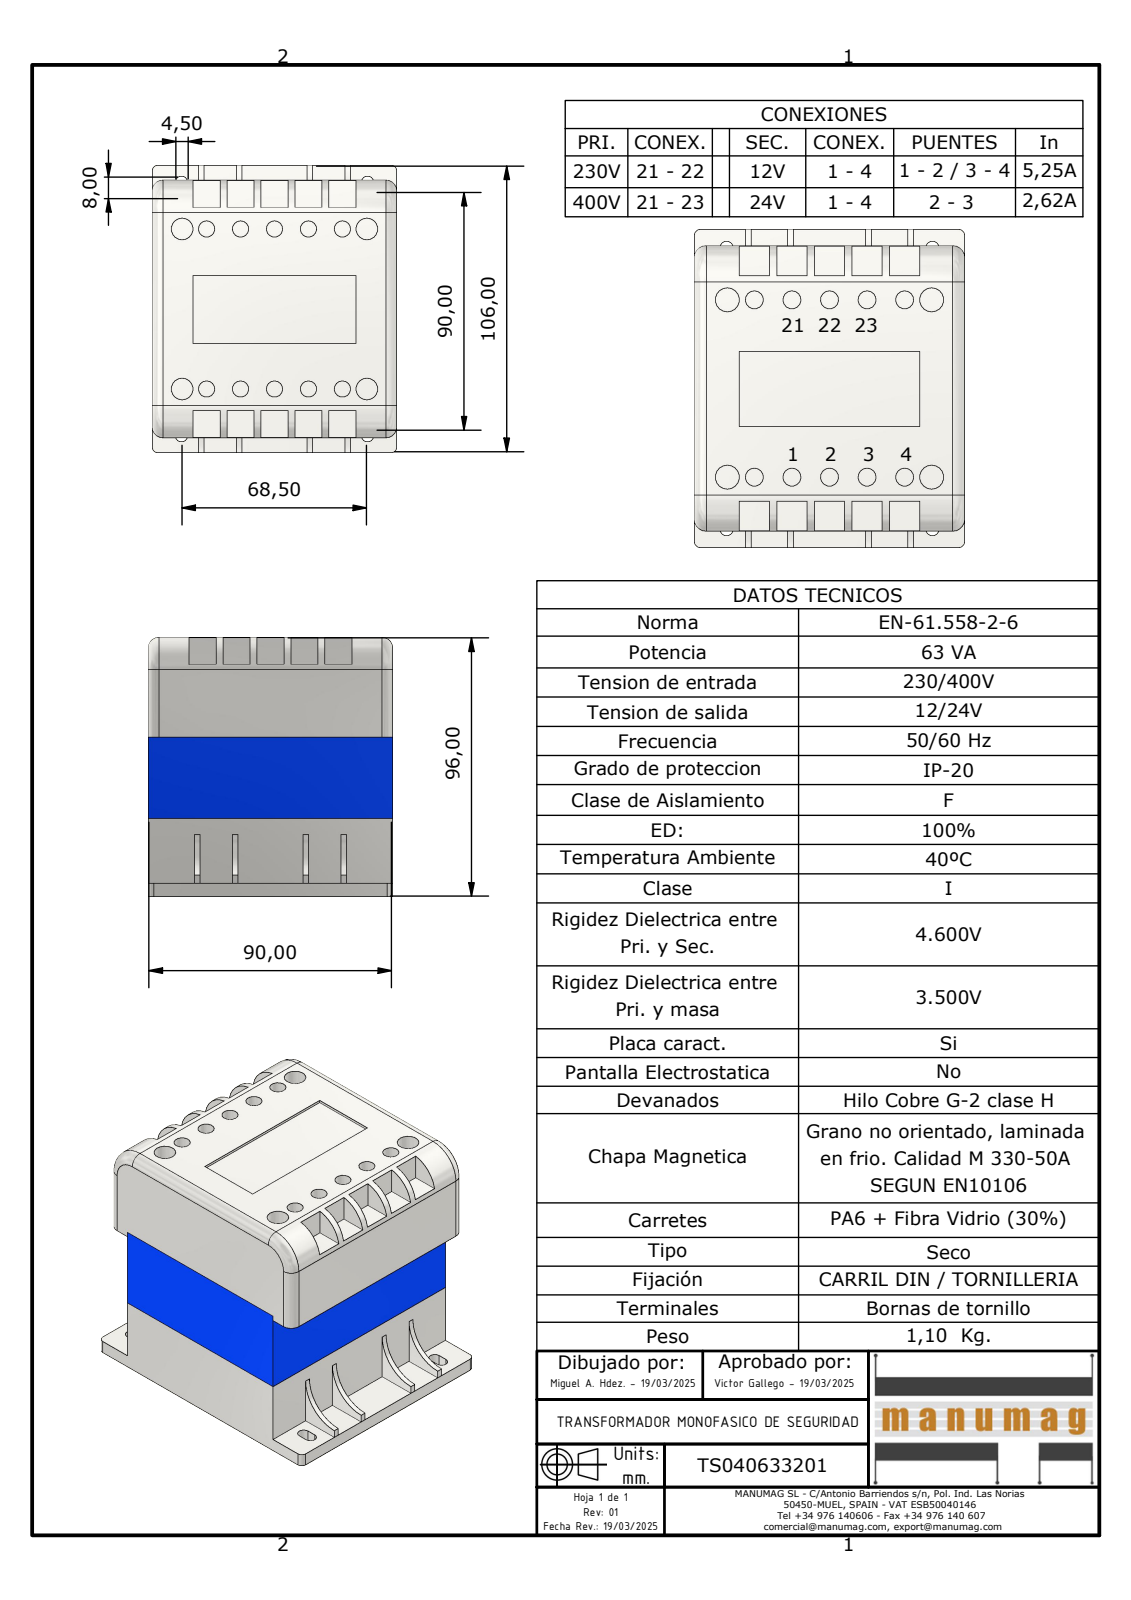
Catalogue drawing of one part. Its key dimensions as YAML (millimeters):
part_name: "TS040633201; CENTRAL EI84-30; SUPERIOR EI84; INFERIOR EI84"
step_written_by: "Autodesk Inventor 2023 (AUTOMOTIVE_DESIGN)"
units: millimeters
bodies: {solids: 11, faces: 188, planar: 142, cylindrical: 42, other: 4}
overall_size: [106, 96, 90]
volume: 349677
surface_area: 95183
round_holes:
  - {diameter: 6, count: 10}
  - {diameter: 8, count: 4}
partial_cylinders:
  - {radius: 2.25, count: 8}
  - {radius: 4, count: 6}
  - {radius: 2, count: 4}
  - {radius: 12, count: 2}
  - {radius: 15, count: 2}
face_to_face_distances: [1, 75, 90, 5, 89, 56, 61, 76, 74, 91]
hole_center_spacings: [59, 12.5, 60.31, 25, 64.08, 9, 21.5, 34]
